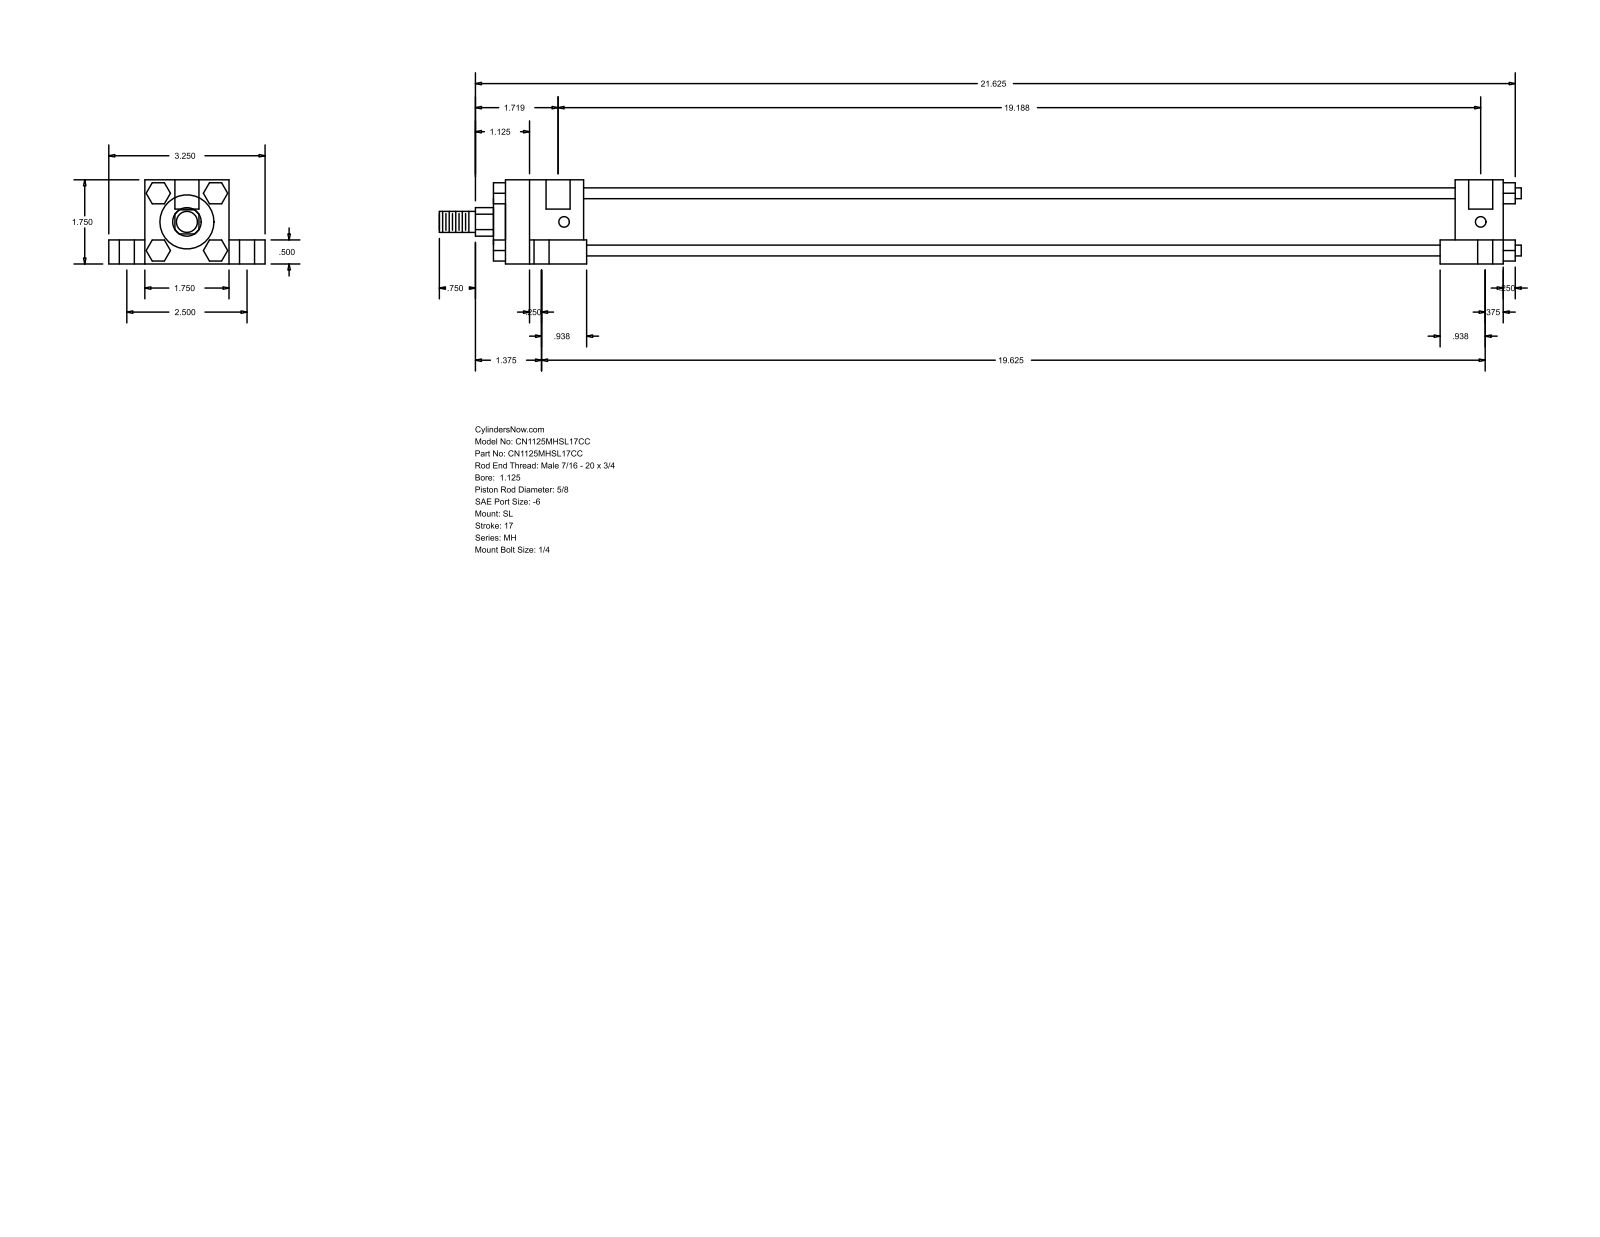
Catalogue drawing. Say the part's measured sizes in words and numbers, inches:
The part is named "MH_SL__0112_0.625". Its 3-D file was written by "GSSL Pune (CONFIG_CONTROL_DESIGN)". It is 0 solids with 150 faces: 114 planar, 36 cylindrical and 0 other. Overall it measures 22.5 by 3.25 by 1.75 inches. Round holes: 4 of diameter 0.219, 4 of diameter 0.313, 4 of diameter 0.563, 2 of diameter 0.5. Round bosses or shafts: 4 of diameter 0.225, 1 of diameter 1.375, 1 of diameter 1.125, 1 of diameter 0.625, 1 of diameter 0.437. Partial cylindrical surfaces (rounded edges, fillets, slot ends): 1 of radius 0.297. The main face-to-face distances are 1.75, 0.75, 0.5, 1.25, 2.5, 0.25, 21, 0.437, 1.875, 1. The hole center spacings are 1.254, 1.269, 1.296, 2.5, 19.063, 19.197, 19.322, 19.446.
